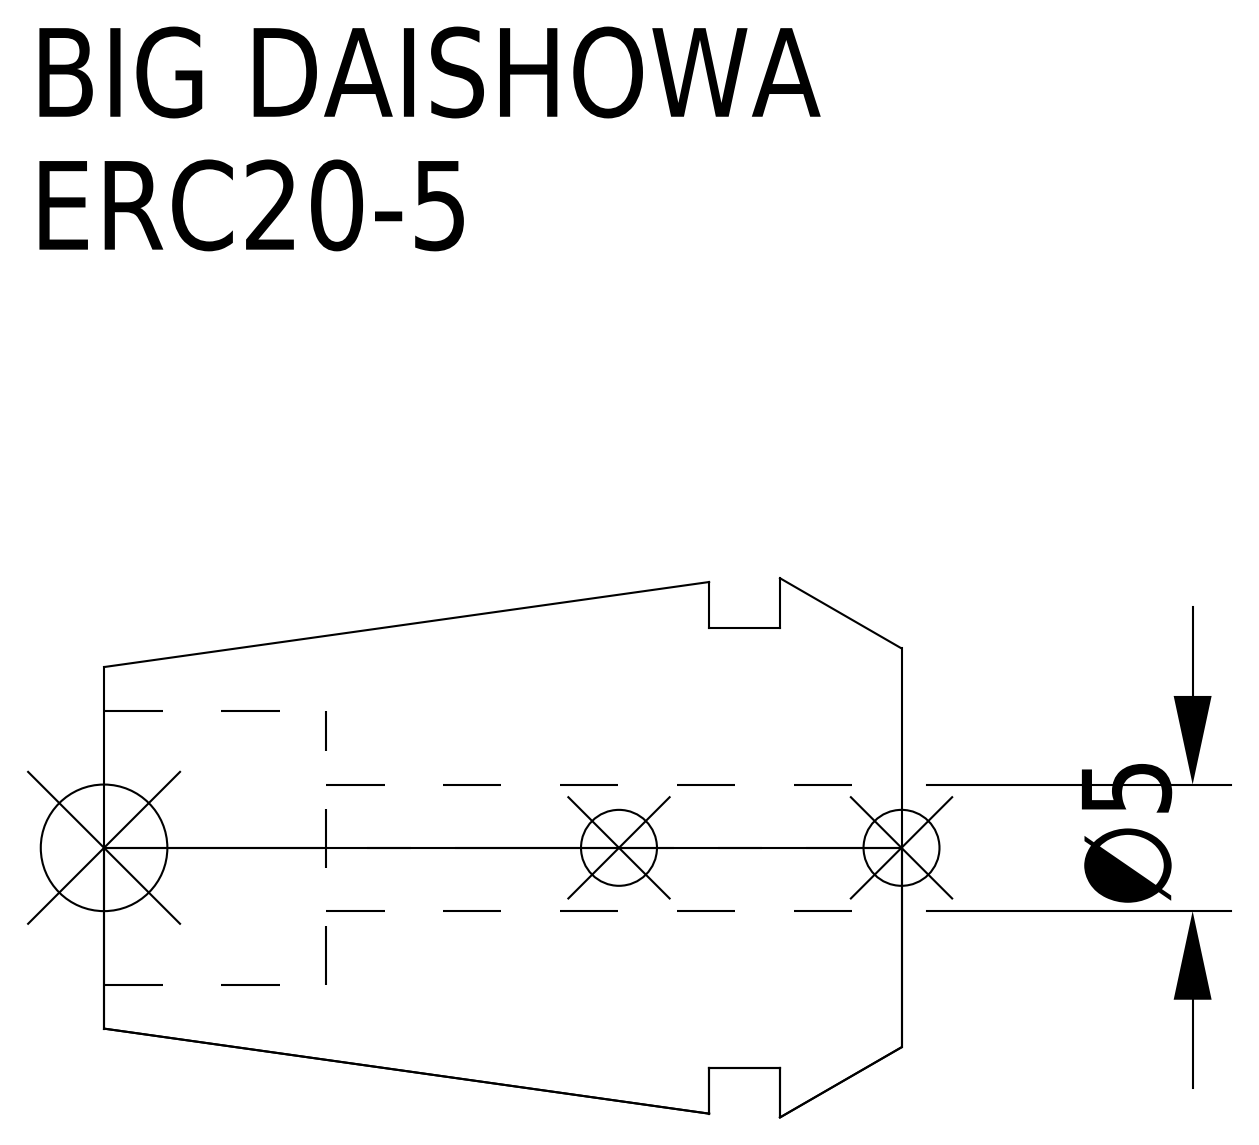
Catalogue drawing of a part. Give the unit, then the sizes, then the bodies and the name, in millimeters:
Units: millimetres
Overall size (bounding box): 31.5 × 21.3 × 21.3
Round holes (diameter × count): ⌀5 ×1, ⌀10.8 ×1
Round bosses / shafts (diameter × count): ⌀17.4 ×1
Main face-to-face distances: 4.8, 7.6, 2.8, 22.73, 17.93, 15.13, 31.5, 26.7, 23.9, 8.77
Volume: 6 633 mm³ · Surface area: 3 011 mm²
Bodies: 1 solid, 15 faces (5 planar, 6 cylindrical, 4 other)
Part name (STEP PRODUCT): ERC20-5
STEP written by: CREO PARAMETRIC BY PTC INC, 2016380 (AUTOMOTIVE_DESIGN)
